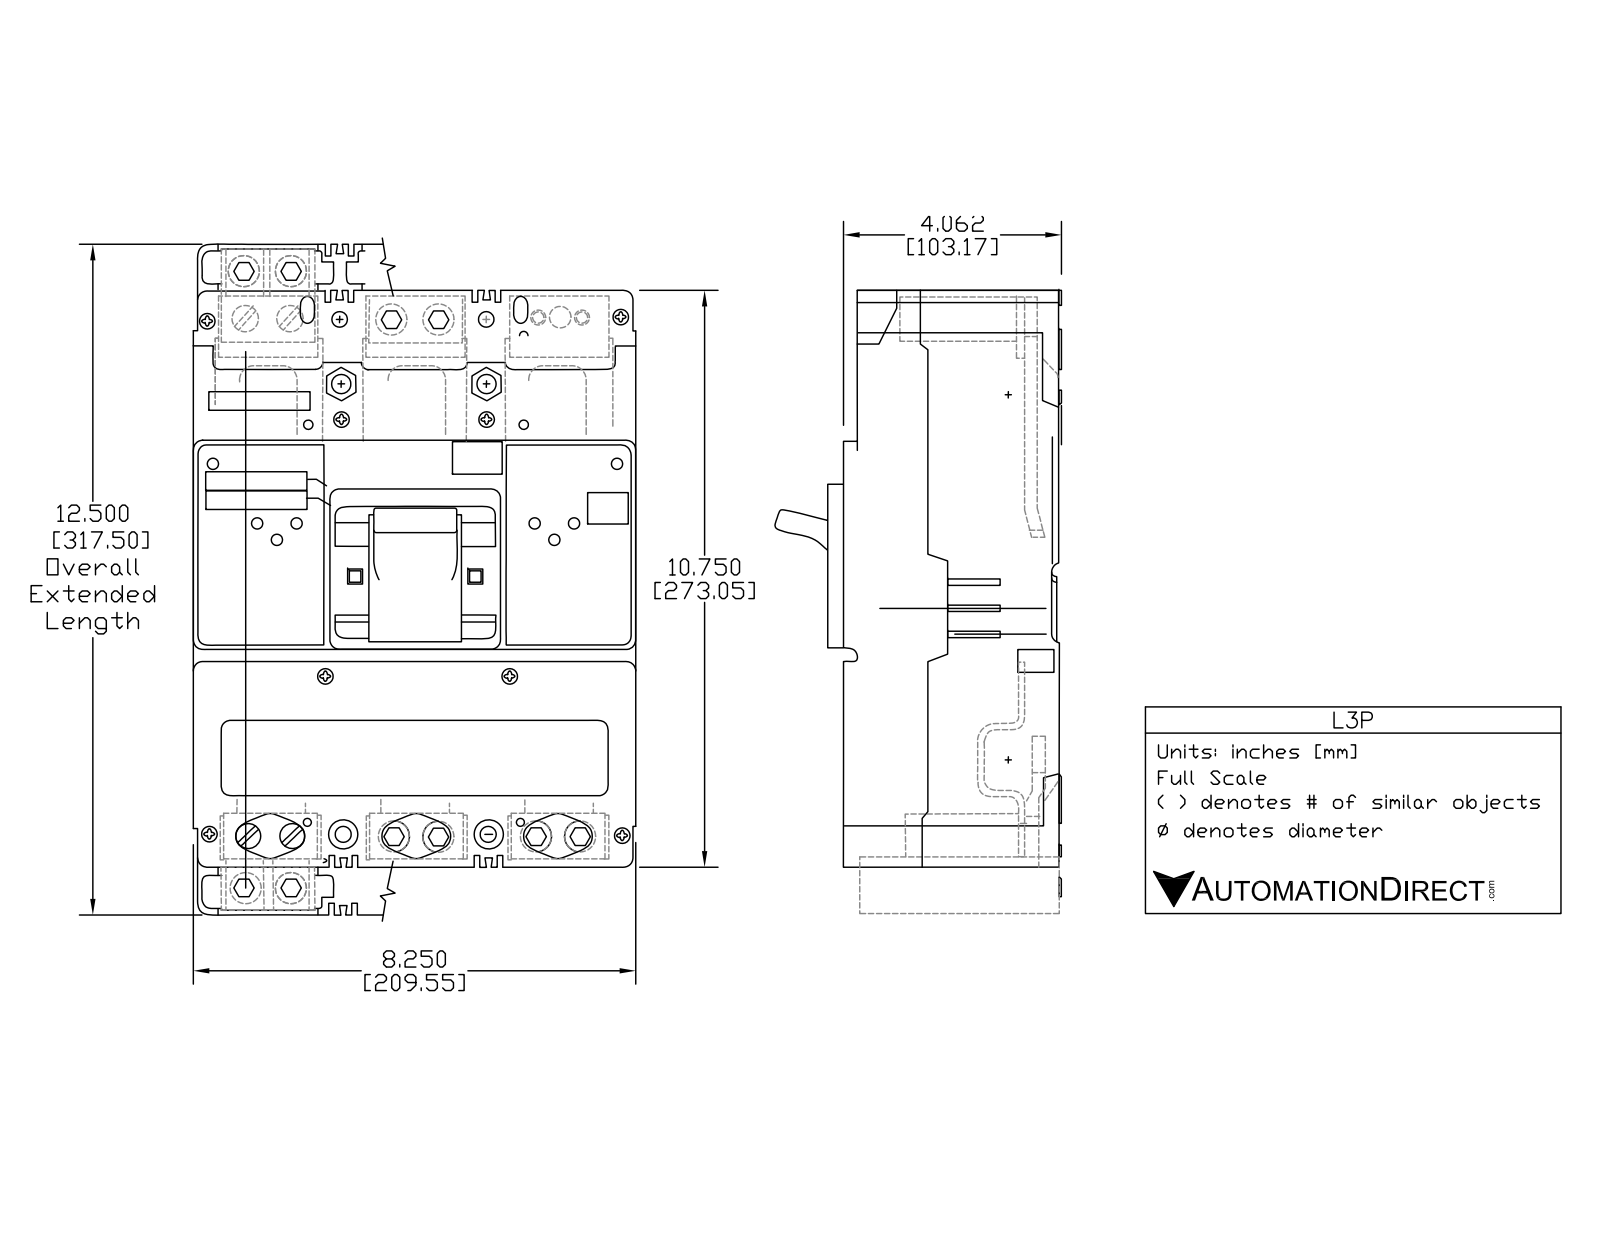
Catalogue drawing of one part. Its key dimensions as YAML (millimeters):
part_name: "L3P-500"
step_written_by: "SolidWorks 2013 (AUTOMOTIVE_DESIGN)"
units: millimeters
bodies: {solids: 67, faces: 1195, planar: 927, cylindrical: 207, other: 61}
overall_size: [273.05, 209.55, 139.2]
volume: 5221000
surface_area: 587257
round_holes:
  - {diameter: 8.66, count: 10}
  - {diameter: 10.5, count: 6}
  - {diameter: 18, count: 6}
  - {diameter: 13.5, count: 5}
  - {diameter: 3, count: 4}
  - {diameter: 7.5, count: 4}
  - {diameter: 10, count: 3}
  - {diameter: 6.35, count: 2}
  - {diameter: 14.4, count: 2}
round_bosses_or_shafts:
  - {diameter: 8, count: 8}
  - {diameter: 9.75, count: 1}
partial_cylinders:
  - {radius: 8, count: 14}
  - {radius: 10, count: 6}
  - {radius: 5, count: 5}
  - {radius: 3, count: 4}
  - {radius: 3.38, count: 4}
  - {radius: 4, count: 4}
  - {radius: 4.33, count: 4}
  - {radius: 6, count: 4}
face_to_face_distances: [22, 59.43, 9, 37.43, 13, 46.43, 209.55, 1, 73.5, 95.5]
hole_center_spacings: [69.85, 178.51, 206.19, 219.45, 247.28, 28.15, 213.94, 242.09]
